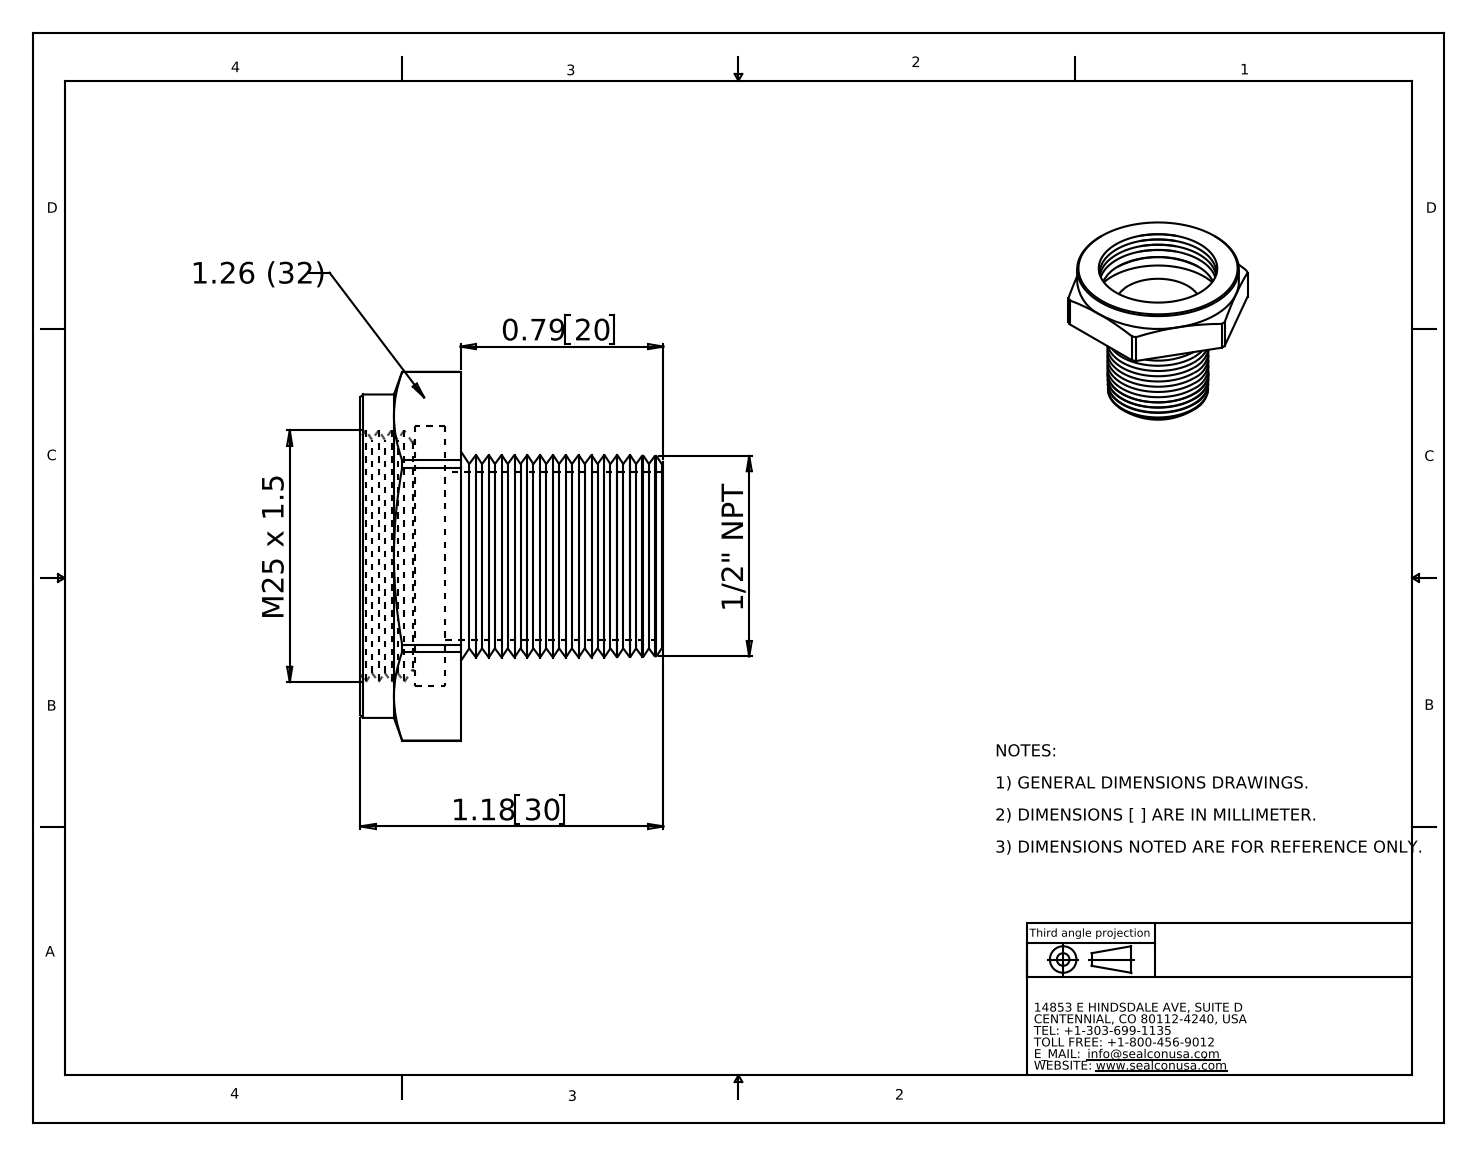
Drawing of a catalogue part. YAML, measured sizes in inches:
part_name: "AT-1225-BR"
step_written_by: "SolidWorks 2008 (CONFIG_CONTROL_DESIGN)"
units: inches
bodies: {solids: 1, faces: 123, planar: 11, cylindrical: 13, other: 99}
overall_size: [1.436, 1.26, 1.18]
volume: 0.341
surface_area: 10.31
round_holes:
  - {diameter: 0.656, count: 1}
  - {diameter: 1.014, count: 1}
round_bosses_or_shafts:
  - {diameter: 1.26, count: 1}
partial_cylinders:
  - {radius: 0.718, count: 1}
face_to_face_distances: [0.39, 1.26, 0.059, 0.331, 0.177, 0.118, 0.213, 0.79, 0.849, 0.967]
